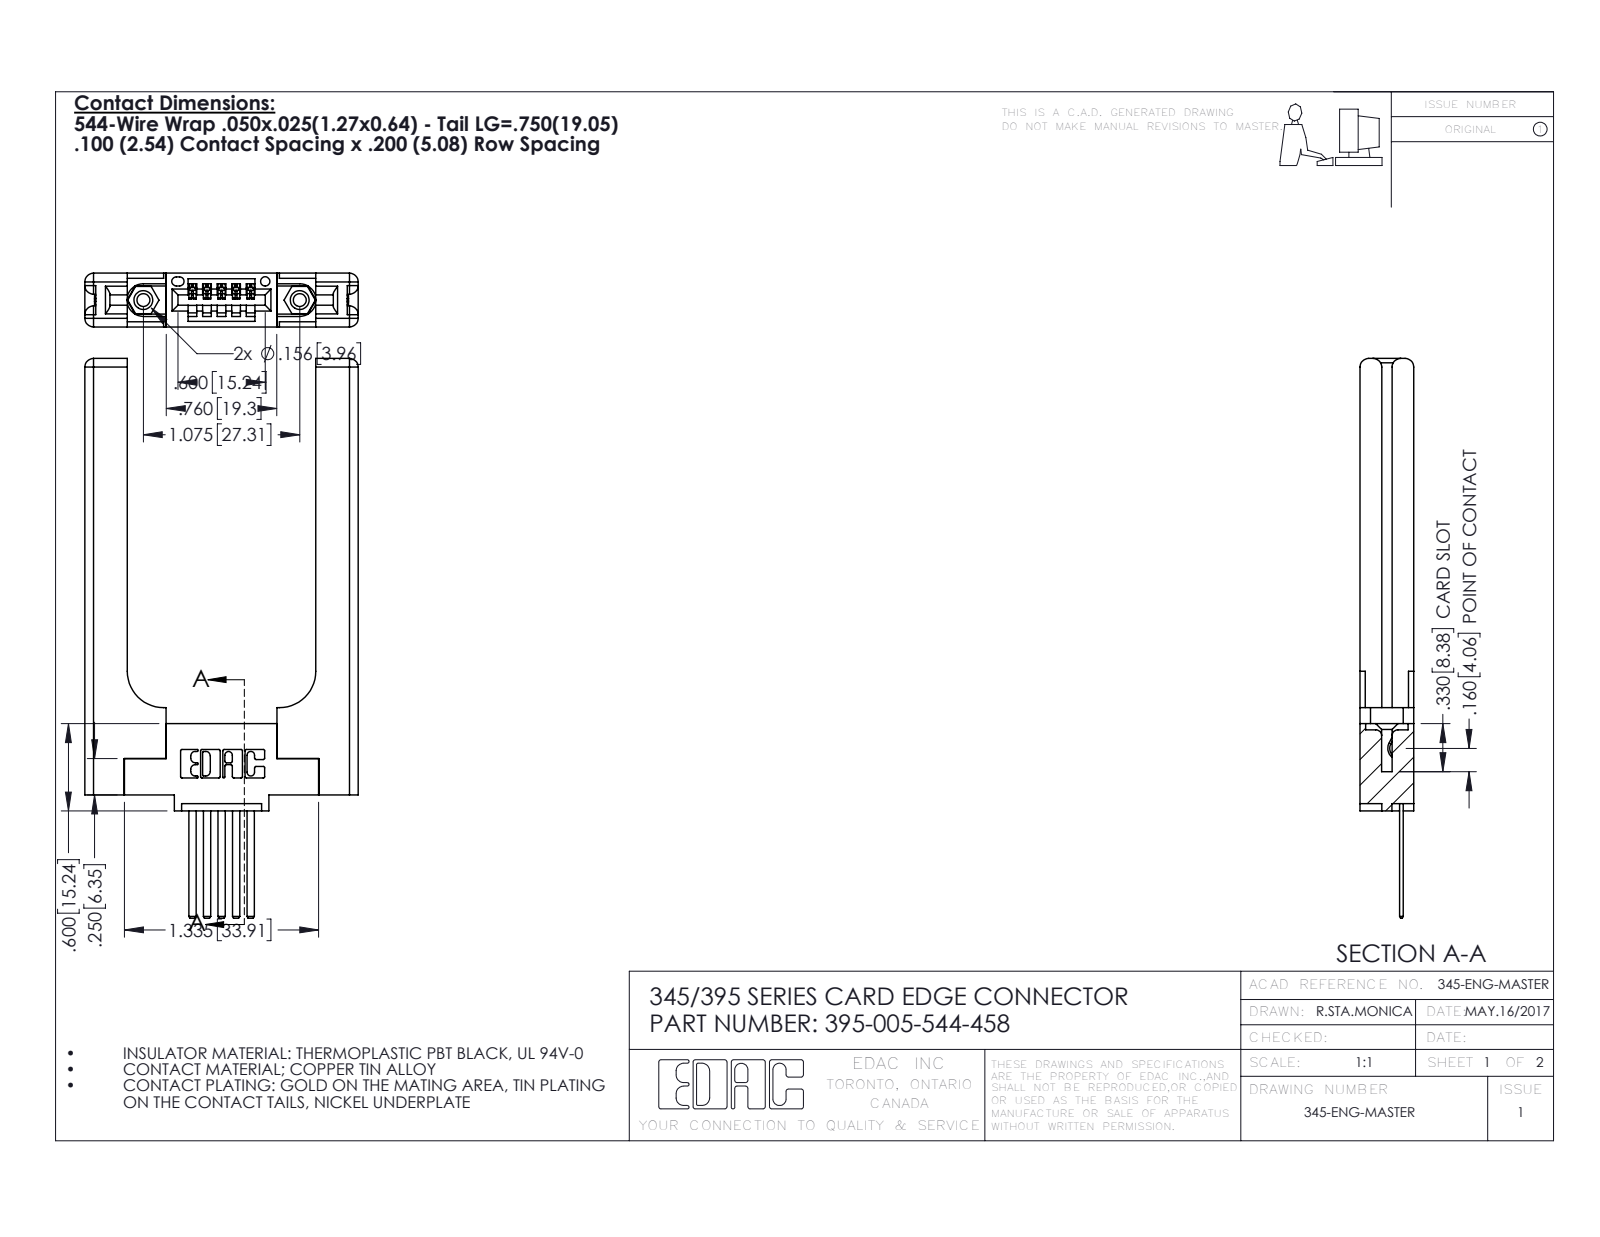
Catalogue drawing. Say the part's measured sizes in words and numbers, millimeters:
The part is named "395-005-544-458; 345-292-001_345-293-144; 345 Part_0.110 Offset - 0.156 Dia-TH; 345-250-001_345-250-001-102 (+1 more)". Its 3-D file was written by "SolidWorks 2016 (CONFIG_CONTROL_DESIGN)". It is 10 solids with 646 faces: 412 planar, 174 cylindrical and 60 other. Overall it measures 97.7 by 47.7 by 9.4 millimeters. Its volume is 12 700 cubic millimeters and its surface area 10 660 square millimeters. Round holes: 2 of diameter 2.3, 2 of diameter 3.2, 2 of diameter 4, 1 of diameter 1.6. Round bosses or shafts: 2 of diameter 3.9. Partial cylindrical surfaces (rounded edges, fillets, slot ends): 22 of radius 0.3, 16 of radius 1.5, 10 of radius 0.2, 6 of radius 0.2, 6 of radius 0.8, 3 of radius 0.7, 2 of radius 0.8, 2 of radius 0.8. The main face-to-face distances are 9.4, 3.8, 5.6, 1.8, 3.8, 2, 7.6, 32.9, 1.8, 7.4. The hole center spacings are 6.9, 21.5, 27.3.
